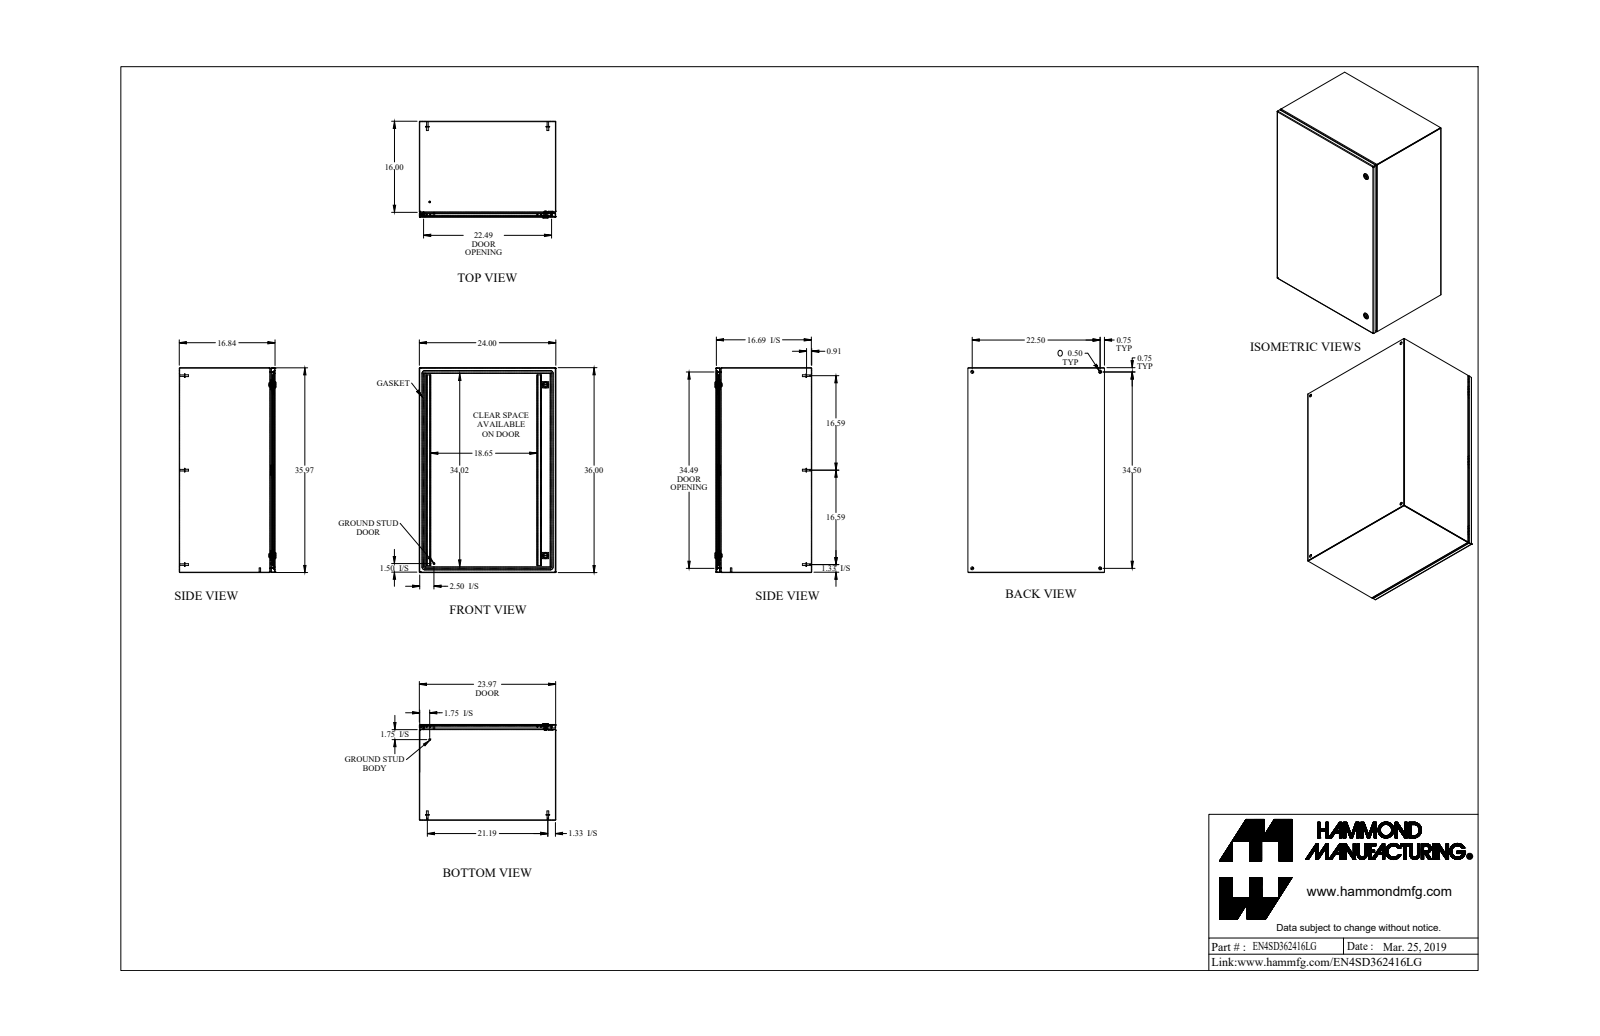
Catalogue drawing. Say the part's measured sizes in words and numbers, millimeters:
The part is named "EN4SD362416LG". Its 3-D file was written by "SolidWorks 2019 (AUTOMOTIVE_DESIGN)". It is 35 solids with 901 faces: 434 planar, 295 cylindrical and 172 other. Overall it measures 914.4 by 609.6 by 431.7 millimeters. Its volume is 4 842 000 cubic millimeters and its surface area 5 349 000 square millimeters. Round holes: 4 of diameter 12.7, 2 of diameter 5.9, 2 of diameter 15.9, 2 of diameter 19.9, 1 of diameter 4.4, 1 of diameter 6.1, 1 of diameter 6.1. Round bosses or shafts: 6 of diameter 15.9, 6 of diameter 8, 6 of diameter 6.9, 2 of diameter 27.9, 2 of diameter 13.3, 2 of diameter 7.1, 2 of diameter 6.4, 1 of diameter 11.6. Partial cylindrical surfaces (rounded edges, fillets, slot ends): 18 of radius 0.9, 18 of radius 2.7, 12 of radius 1.1, 12 of radius 2.1, 12 of radius 7.9, 6 of radius 0.2, 6 of radius 1.6, 4 of radius 3.2. The main face-to-face distances are 1.8, 425.8, 607.8, 424, 427.7, 912.6, 605.9, 609.6, 910.7, 914.4. The hole center spacings are 571.5, 876.3, 1046.2, 63.3, 63.3, 547.2, 547.2, 762.
